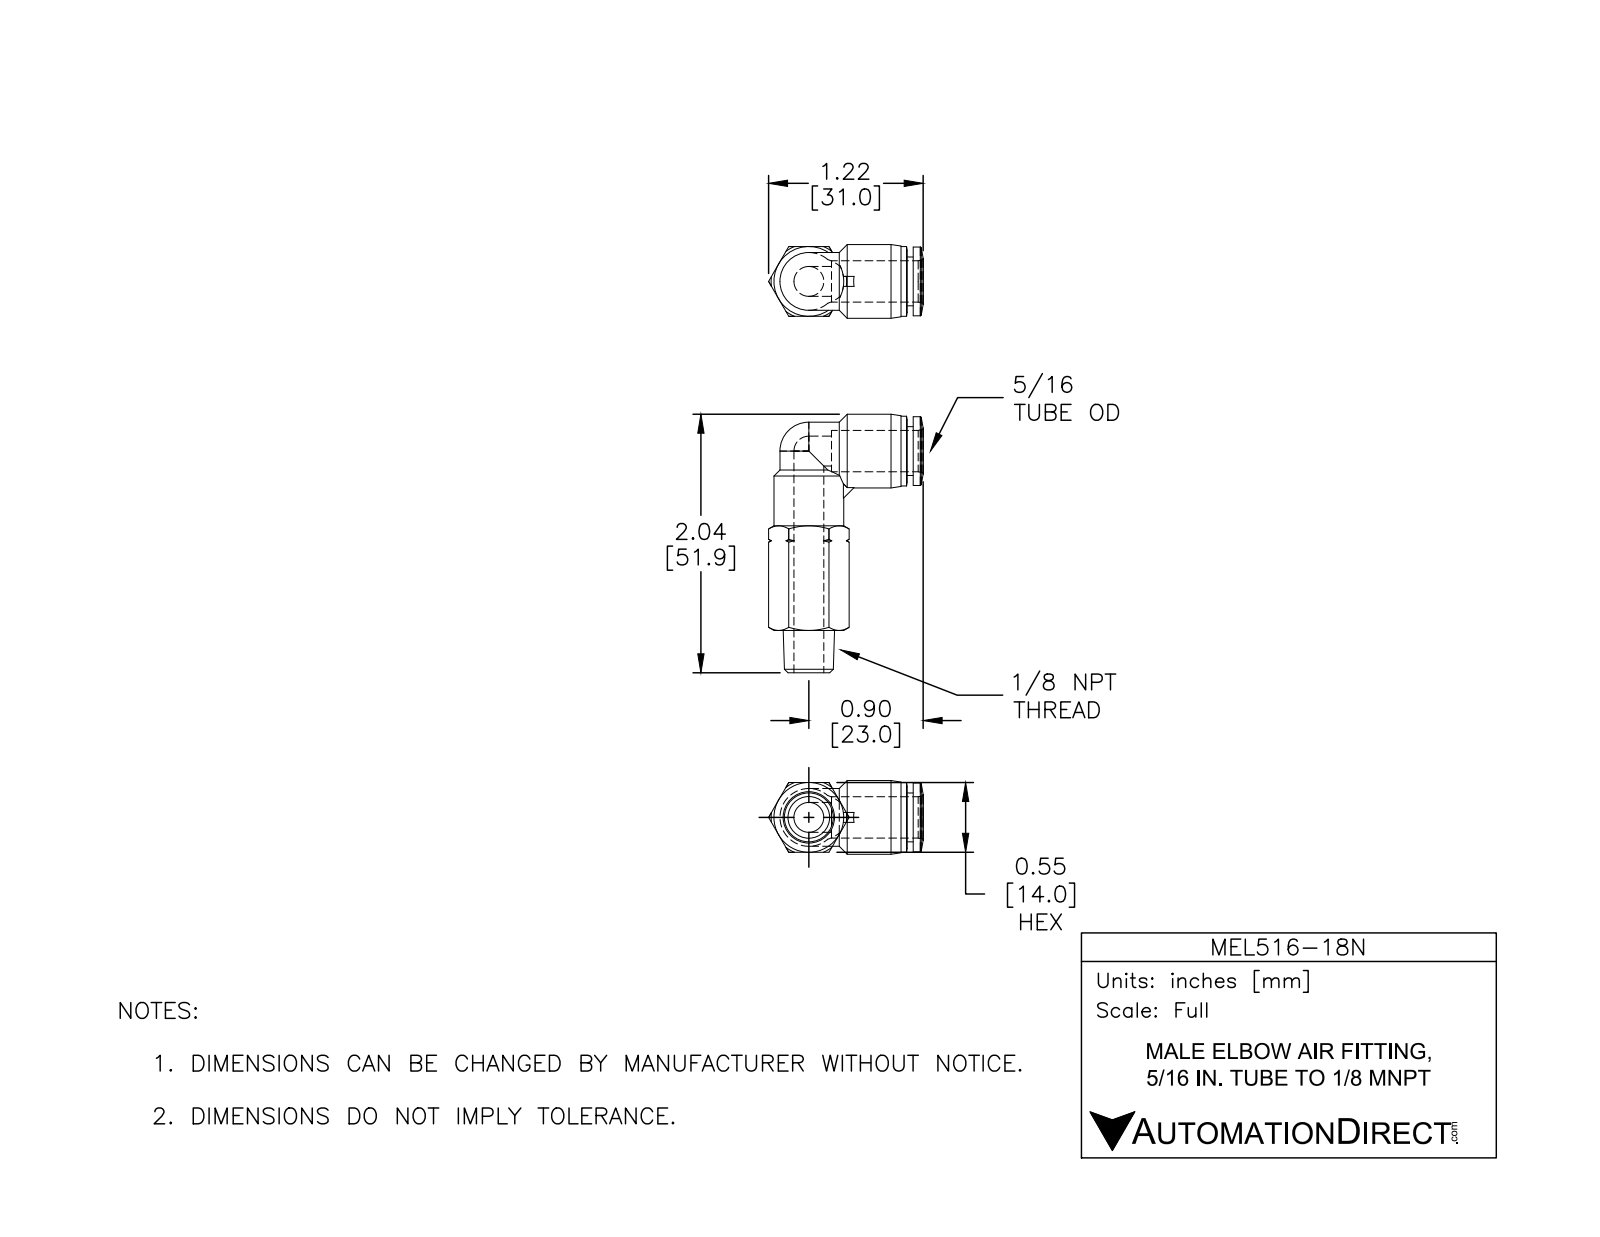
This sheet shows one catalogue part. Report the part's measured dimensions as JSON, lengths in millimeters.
{"part_name": "MEL516-18N", "step_written_by": "SolidWorks 2015 (CONFIG_CONTROL_DESIGN)", "units": "millimeters", "bodies": {"solids": 1, "faces": 87, "planar": 15, "cylindrical": 21, "other": 51}, "overall_size": [51.9, 31, 14.8], "volume_mm3": 7140, "surface_area_mm2": 4648, "round_holes": [[6, 2], [8.3, 1]], "round_bosses_or_shafts": [[14, 2], [14.8, 1], [13.8, 1], [11.6, 1], [9.8, 1]], "partial_cylinders_radius": [[5.8, 1]], "face_to_face_distances": [14, 1.2, 8.5, 15.2, 16.4, 6, 8, 13.9, 1.2, 2.4]}
